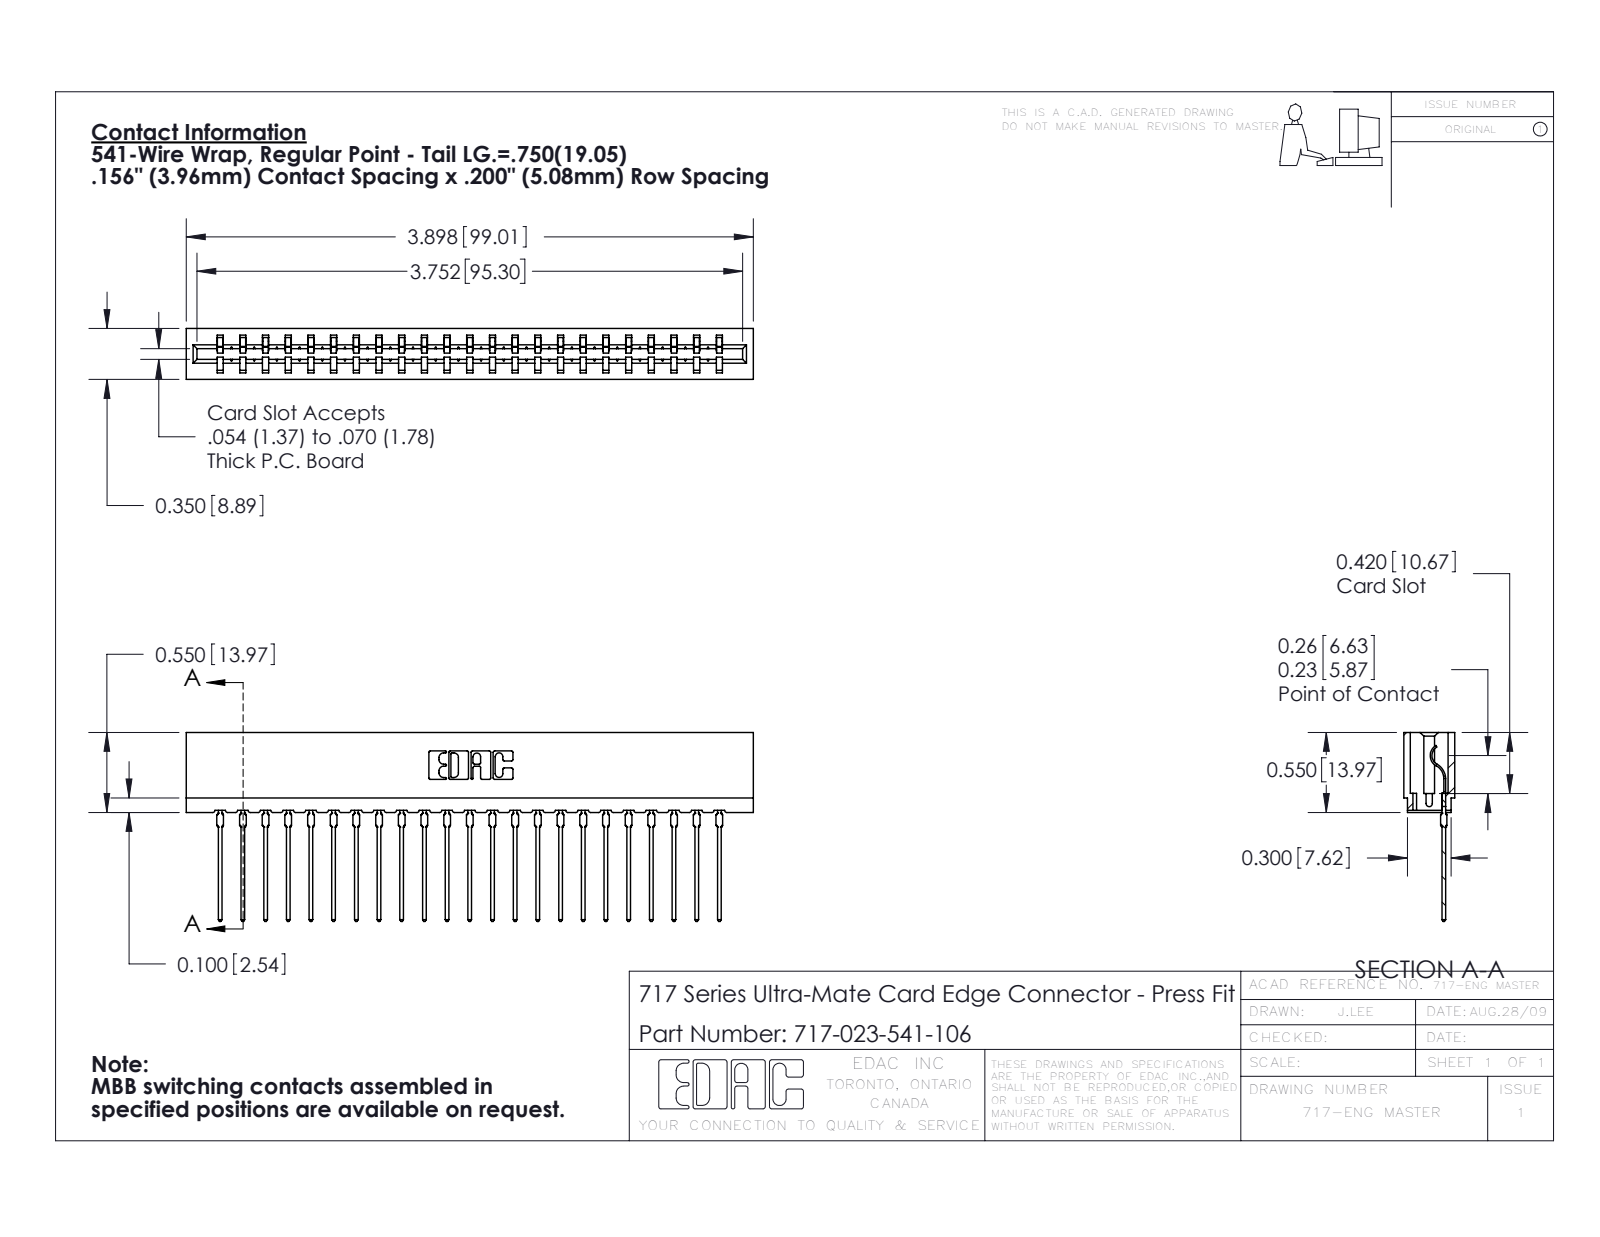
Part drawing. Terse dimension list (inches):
name: 717 Part_Insulator Option - 06; 717-023-541-106; 745-292-001_541
written by: SolidWorks 2016 (CONFIG_CONTROL_DESIGN)
unit: in
bodies: 24 solids, 2693 faces (1618 planar, 477 cylindrical, 598 other)
size: 3.898 × 1.299 × 0.35
volume: 0.521 in³; area: 19.03 in²
rounds: 46× R0.015, 46× R0.021, 22× R0.01, 6× R0.007, 6× R0.031, 4× R0.005, 4× R0.011, 3× R0.026
face distances: 0.212, 0.138, 0.35, 0.156, 0.063, 0.287, 0.076, 0.149, 0.074, 0.624
